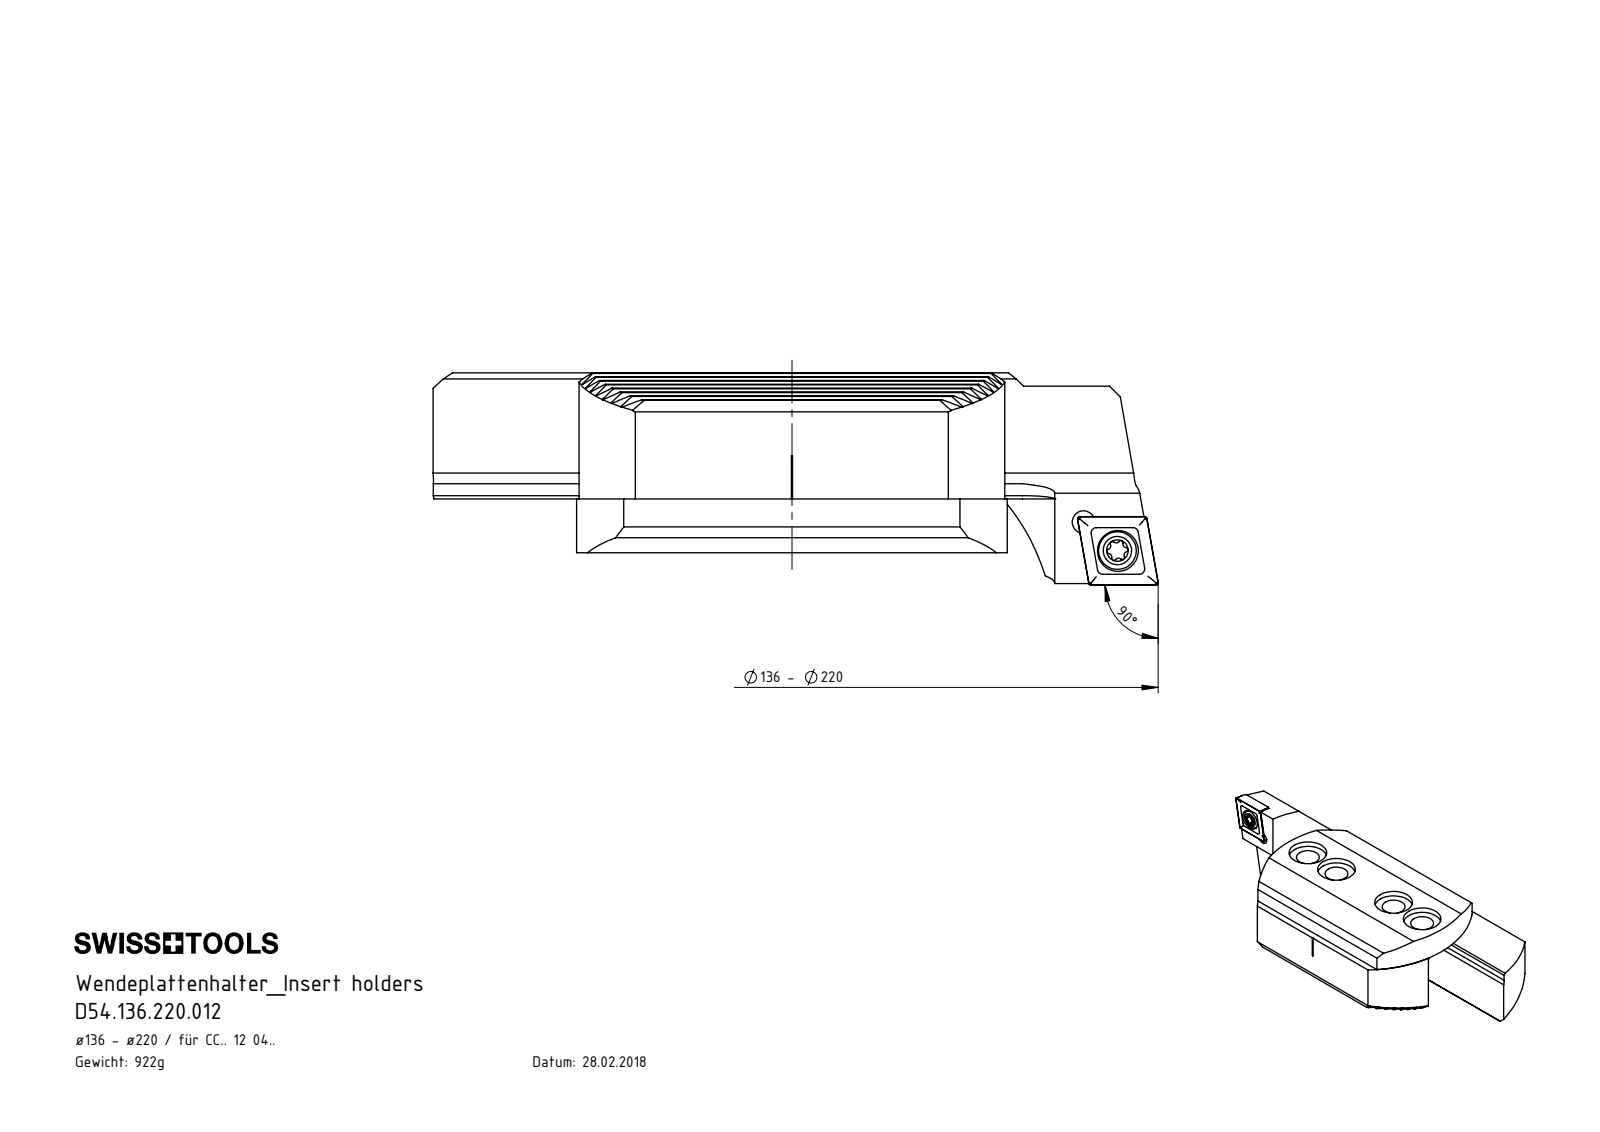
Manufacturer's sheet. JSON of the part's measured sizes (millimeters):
{"part_name": "F00-WCB.136.002_A; F00-WCC.136.001; CCMT120404; WCC-ER2.001.010_A (+3 more)", "step_written_by": "SolidWorks 2017 (CONFIG_CONTROL_DESIGN)", "units": "millimeters", "bodies": {"solids": 5, "faces": 632, "planar": 382, "cylindrical": 68, "other": 182}, "overall_size": [134.59, 55, 39.4], "volume_mm3": 117488, "surface_area_mm2": 32184, "round_holes": [[8.5, 4], [14, 4], [4.2, 2], [5.5, 1], [7.6, 1]], "round_bosses_or_shafts": [[7, 1], [5, 1]], "partial_cylinders_radius": [[0.2, 16], [0.39, 6], [40, 6], [0.69, 3], [0.69, 3], [0.8, 1], [6, 1]], "face_to_face_distances": [2.38, 4.76, 21.3, 33.7, 7.14, 12.4, 9.52, 10, 4.77, 7.15], "hole_center_spacings": [15, 45, 8.21, 8.33, 30, 60]}
